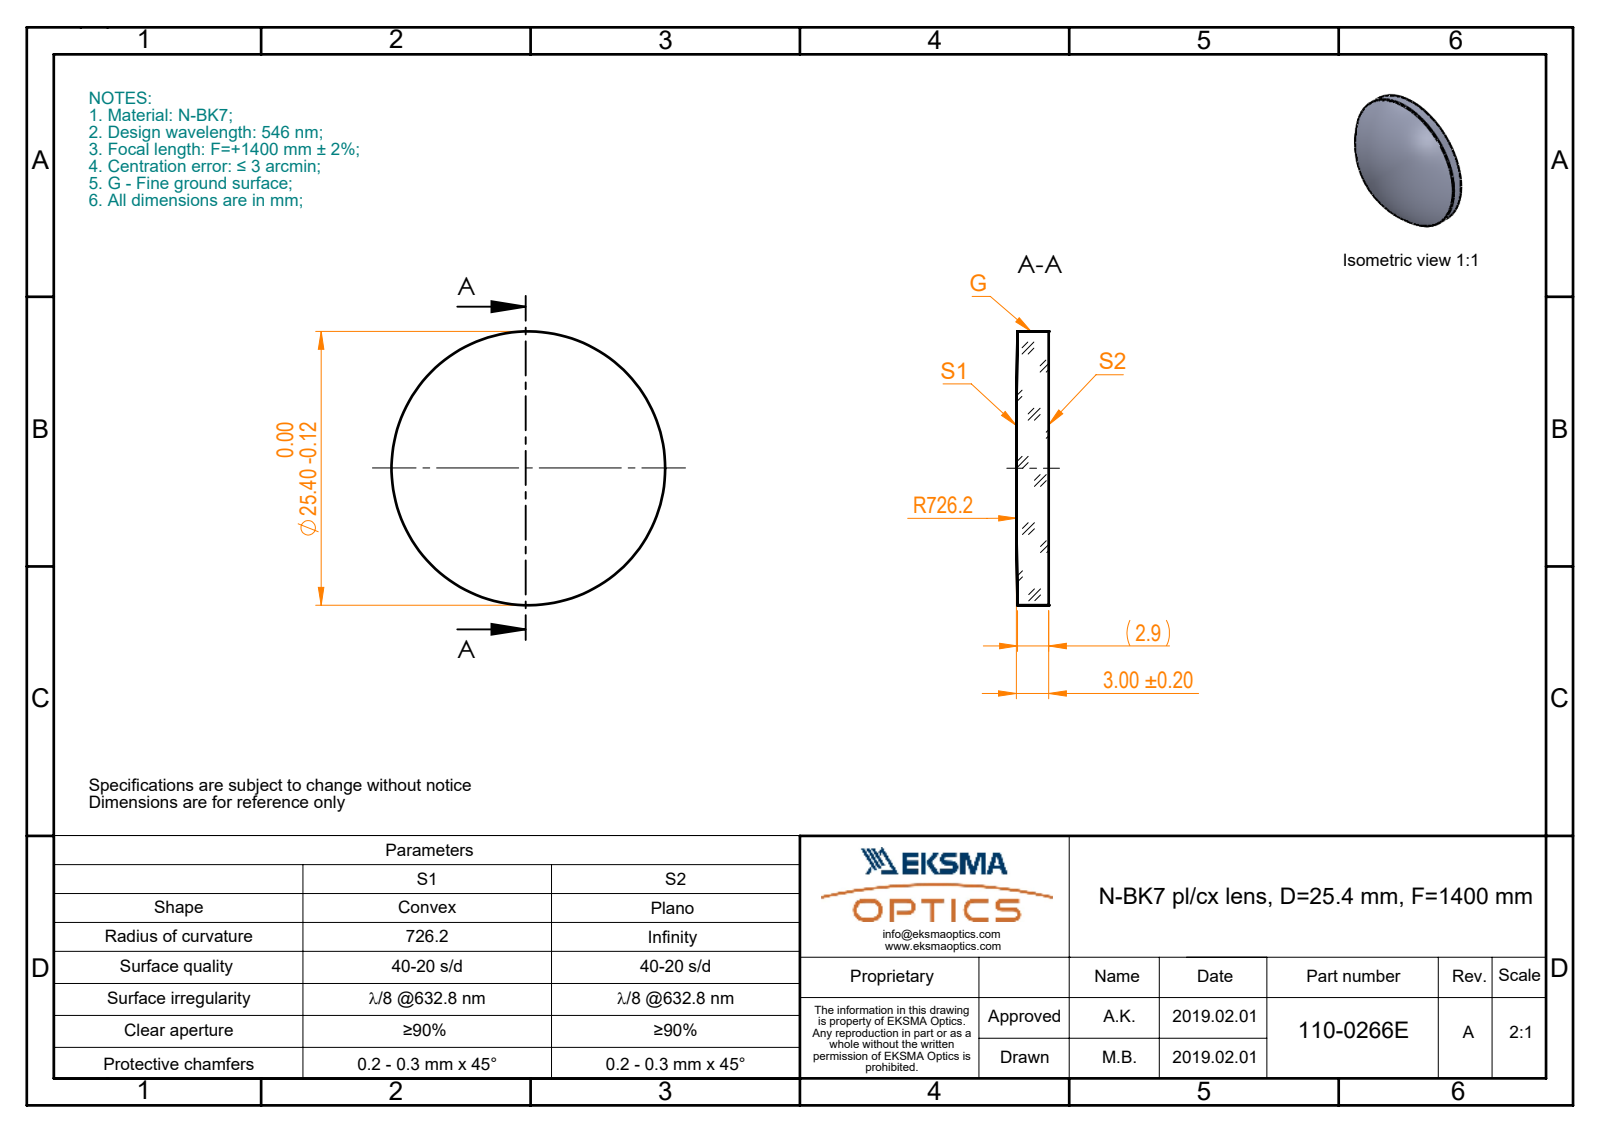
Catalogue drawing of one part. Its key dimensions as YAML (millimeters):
part_name: "110-0266E BK7 pl-cx 25.4 F1400"
step_written_by: "SolidWorks 2017 (CONFIG_CONTROL_DESIGN)"
units: millimeters
bodies: {solids: 1, faces: 5, planar: 1, cylindrical: 2, other: 2}
overall_size: [25.4, 25.4, 3]
volume: 1492
surface_area: 1244
round_bosses_or_shafts:
  - {diameter: 25.4, count: 1}
